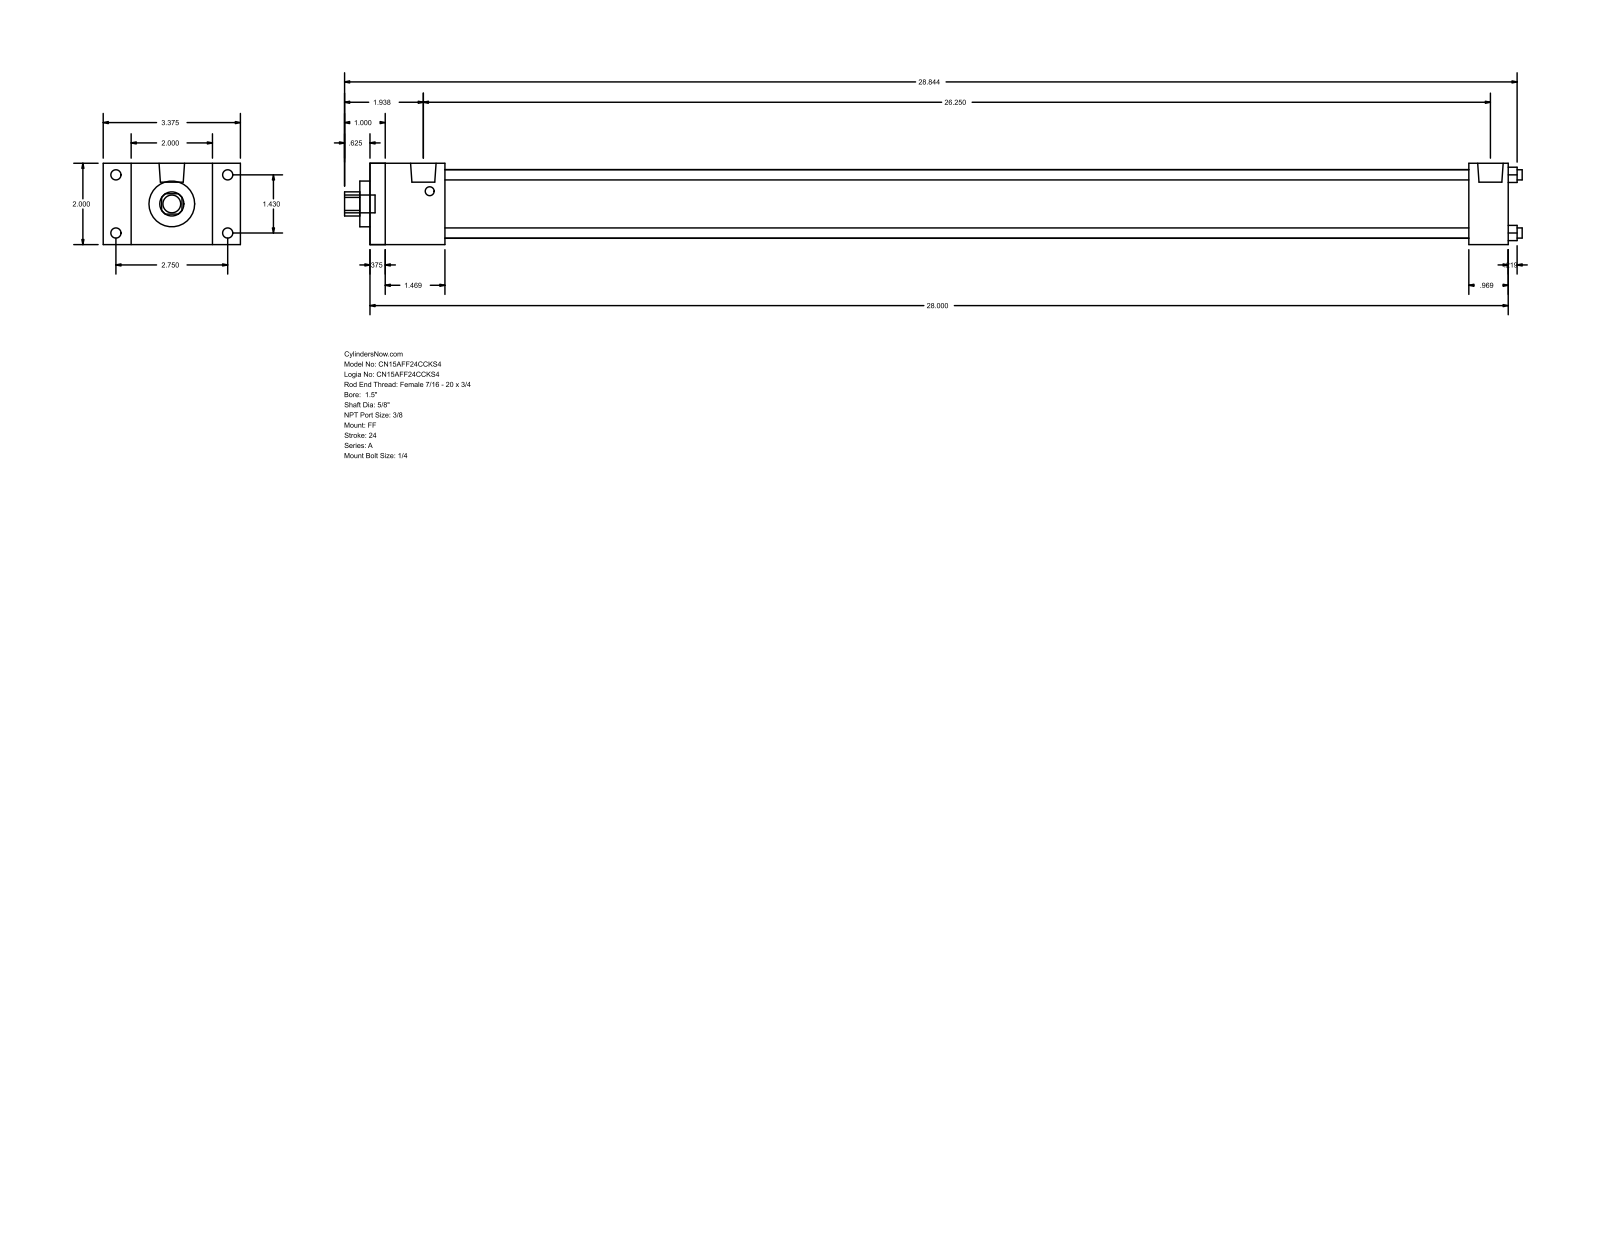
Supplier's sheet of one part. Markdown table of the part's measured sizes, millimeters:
| quantity | value |
| --- | --- |
| part name | A_FF__0150_0.625 |
| STEP written by | GSSL Pune (CONFIG_CONTROL_DESIGN) |
| units | millimeters |
| bodies | 0 solids, 92 faces (64 planar, 28 cylindrical, 0 other) |
| overall size | 735.81 × 85.72 × 50.8 |
| round holes (diameter × count) | 6.35 × 4, 15.88 × 1, 28.57 × 1, 42.93 × 1 |
| round bosses / shafts (diameter × count) | 6.35 × 4, 5.56 × 4, 15.93 × 2, 11.11 × 1 |
| partial cylindrical surfaces (radius × count) | 7.54 × 1 |
| main face-to-face distances | 50.8, 711.2, 9.52, 701.68, 46.83, 686.59, 37.31, 677.07, 639.76, 664.37 |
| hole center spacings | 25.68, 36.32, 51.36 |
